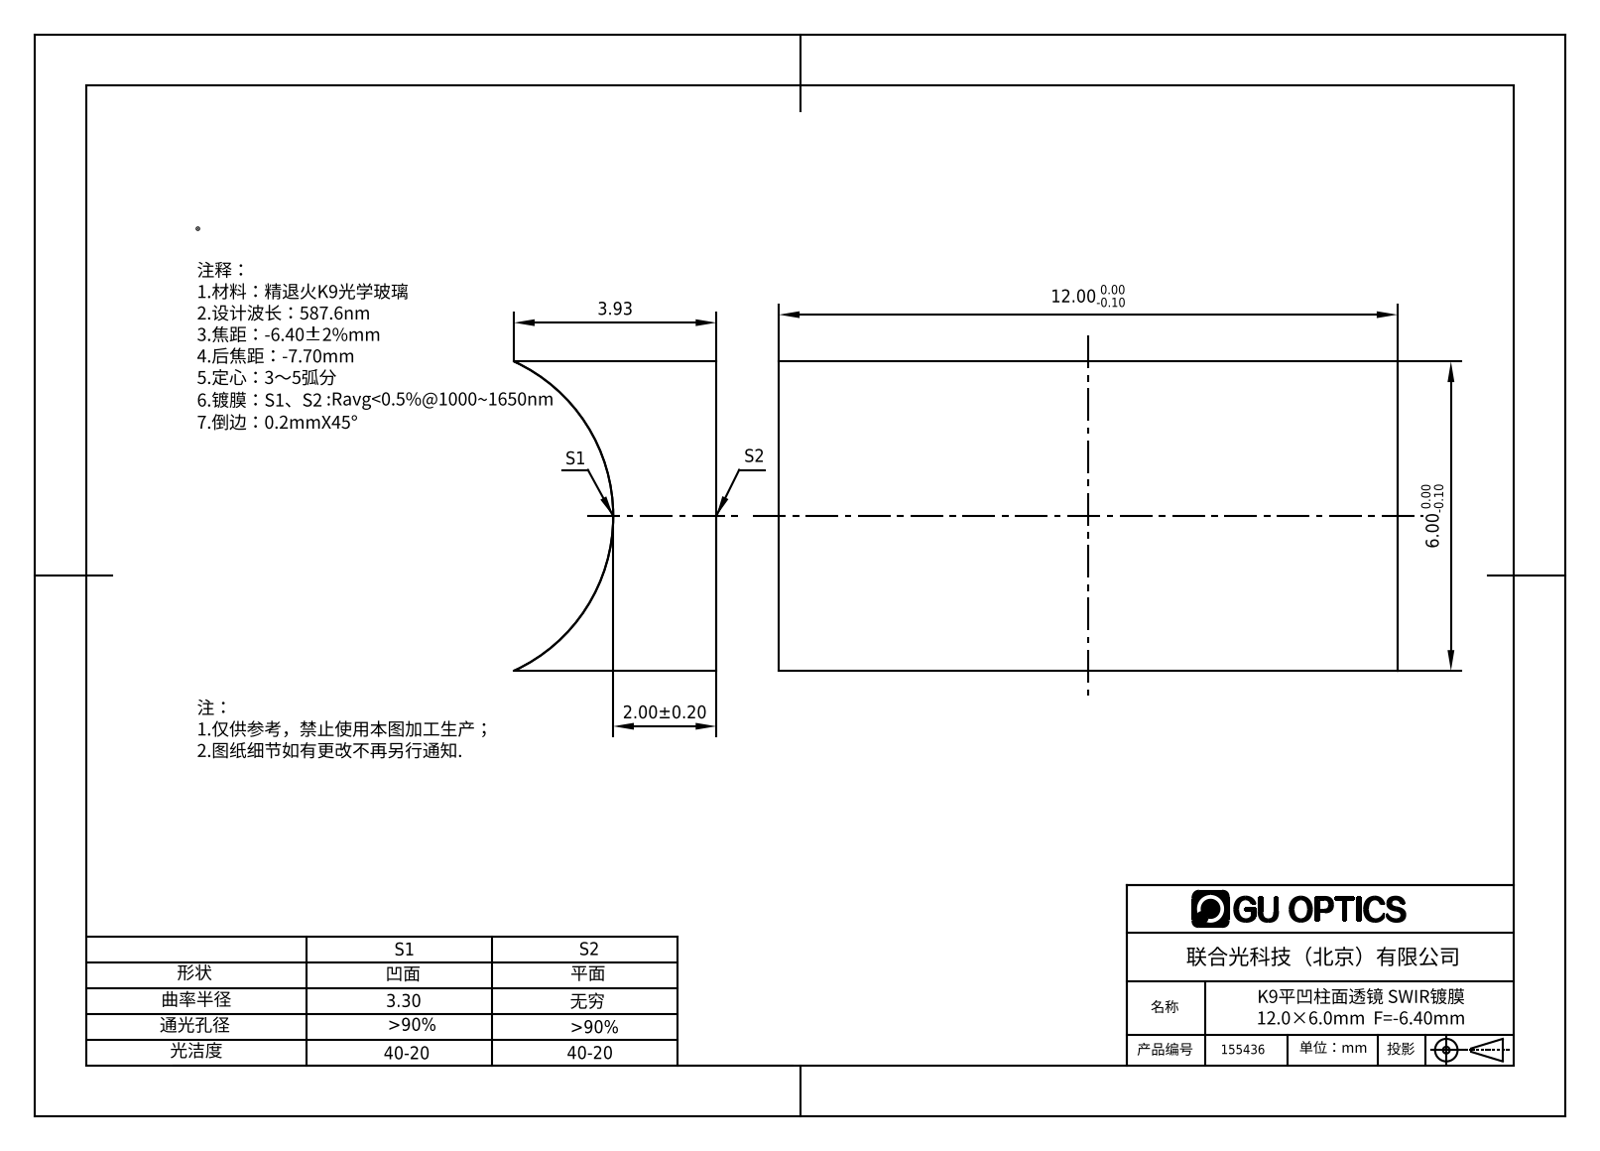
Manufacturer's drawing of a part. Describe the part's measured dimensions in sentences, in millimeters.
The part is named "155337". Its 3-D file was written by "SolidWorks 2016 (AUTOMOTIVE_DESIGN)". It is 1 solid with 6 faces: 5 planar, 1 cylindrical and 0 other. Overall it measures 12 by 6 by 3.92 millimeters. Its volume is 183 cubic millimeters and its surface area 287 square millimeters. Partial cylindrical surfaces (rounded edges, fillets, slot ends): 1 of radius 3.3. The main face-to-face distances are 6, 12.
